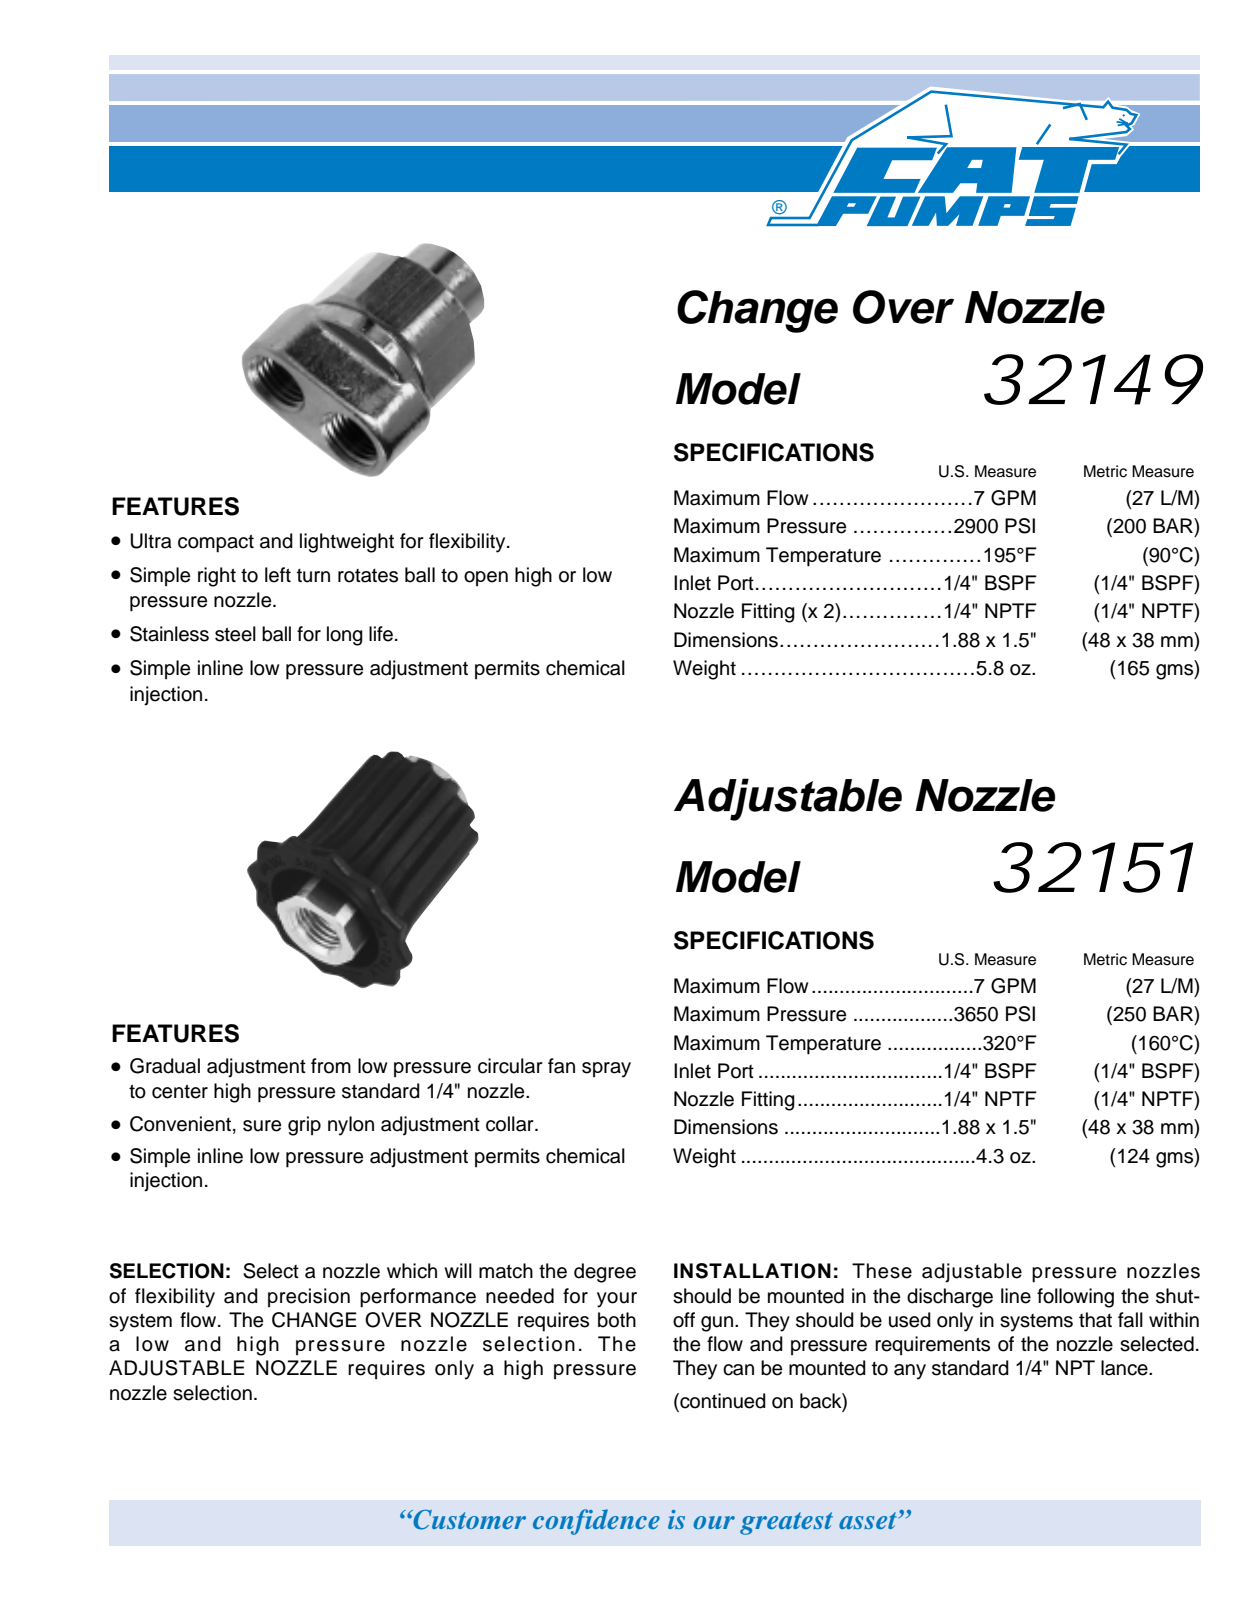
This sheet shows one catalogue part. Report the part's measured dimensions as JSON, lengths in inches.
{"part_name": "32149", "step_written_by": "SolidWorks 2020 (CONFIG_CONTROL_DESIGN)", "units": "inches", "bodies": {"solids": 1, "faces": 76, "planar": 19, "cylindrical": 21, "other": 36}, "overall_size": [1.77, 1.44, 1.258], "volume_in3": 1.289, "surface_area_in2": 11.33, "round_holes": [[0.438, 3]], "round_bosses_or_shafts": [[1.15, 1], [0.75, 1]], "partial_cylinders_radius": [[0.031, 2], [0.383, 2], [0.629, 1]], "face_to_face_distances": [1.178, 1.325, 0.765, 0.445, 1.77, 1.32, 0.875, 0.45, 1.12, 0.675], "hole_center_spacings": [0.337, 0.675]}
